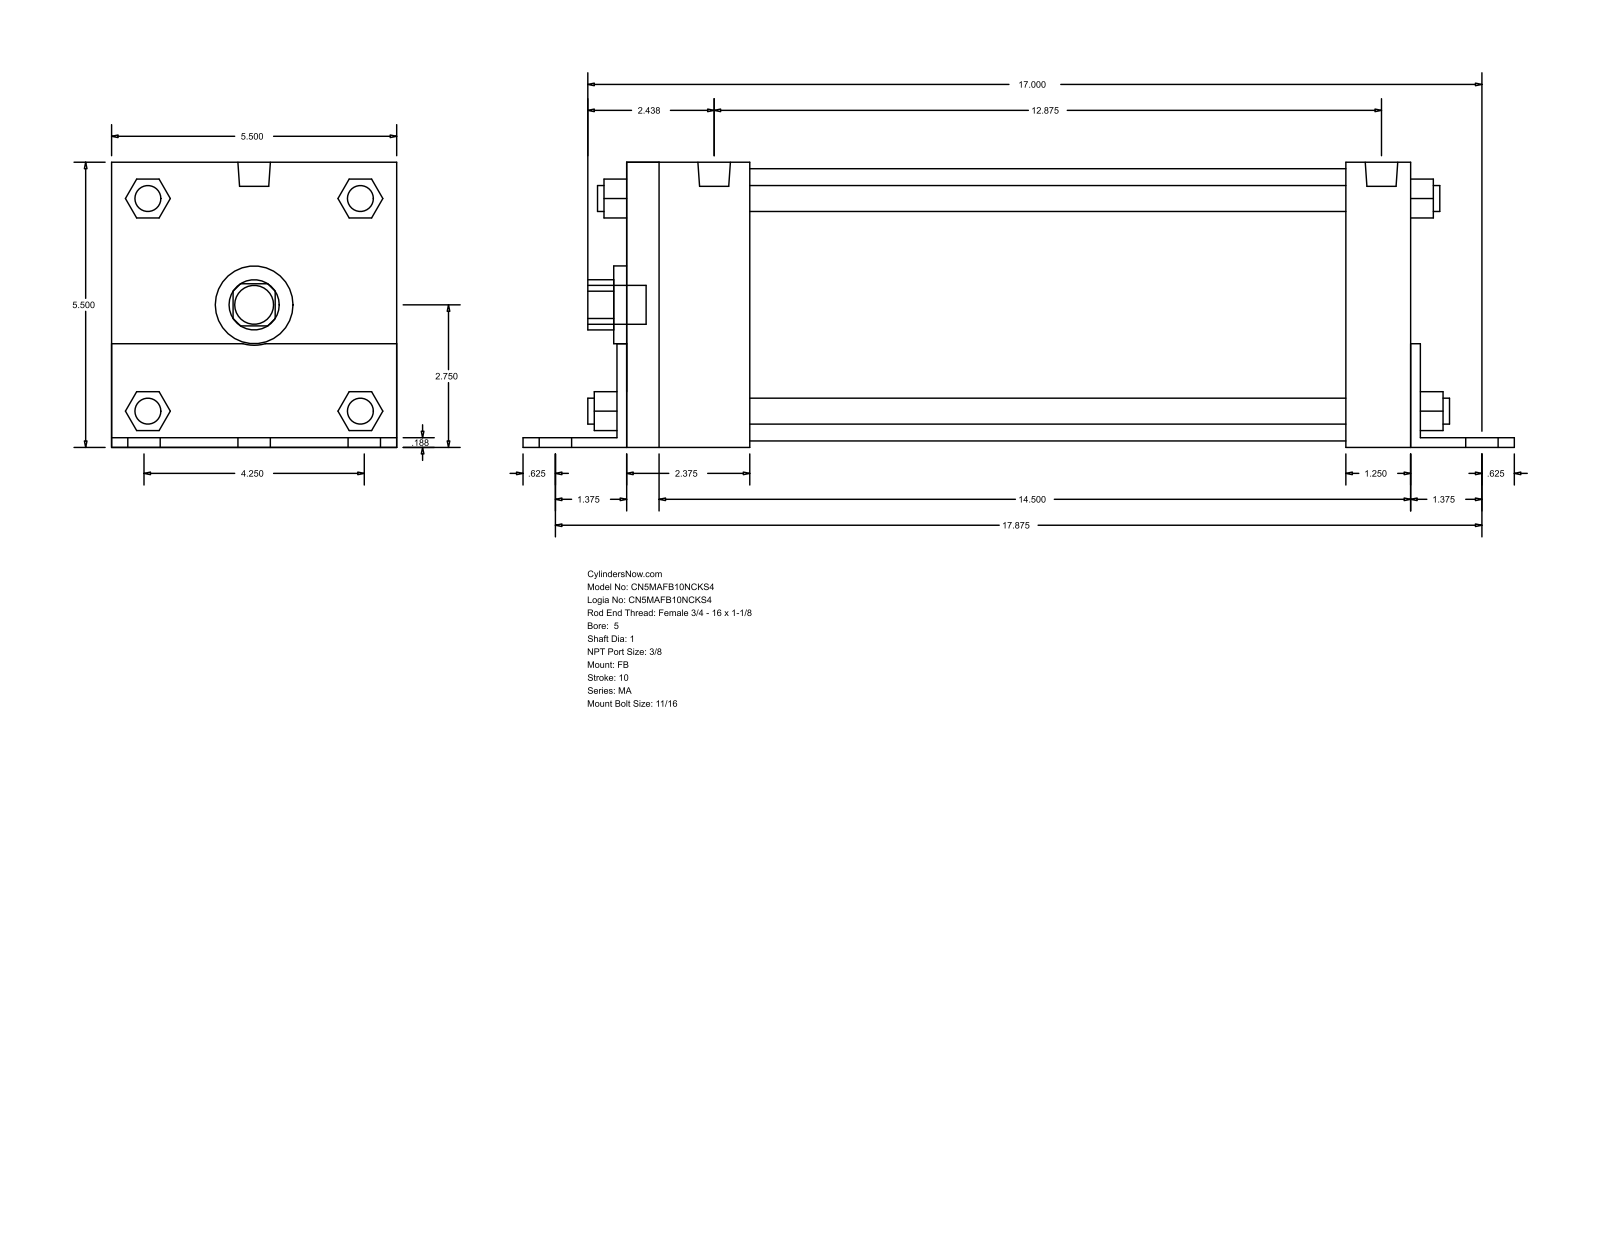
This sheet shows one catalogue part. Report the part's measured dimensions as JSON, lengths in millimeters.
{"part_name": "MA_FB__0500_1", "step_written_by": "GSSL Pune (CONFIG_CONTROL_DESIGN)", "units": "millimeters", "bodies": {"solids": 0, "faces": 140, "planar": 105, "cylindrical": 35, "other": 0}, "overall_size": [485.77, 139.75, 139.7], "round_holes": [[25.4, 1], [38.1, 1], [133.35, 1]], "round_bosses_or_shafts": [[17.46, 6], [12.7, 4], [11.11, 4], [15.93, 2], [19.05, 1]], "partial_cylinders_radius": [[12.29, 1], [19.81, 1]], "face_to_face_distances": [139.7, 4.76, 139.75, 388.94, 4.71, 134.99, 384.18, 393.7, 31.75, 36.51]}
